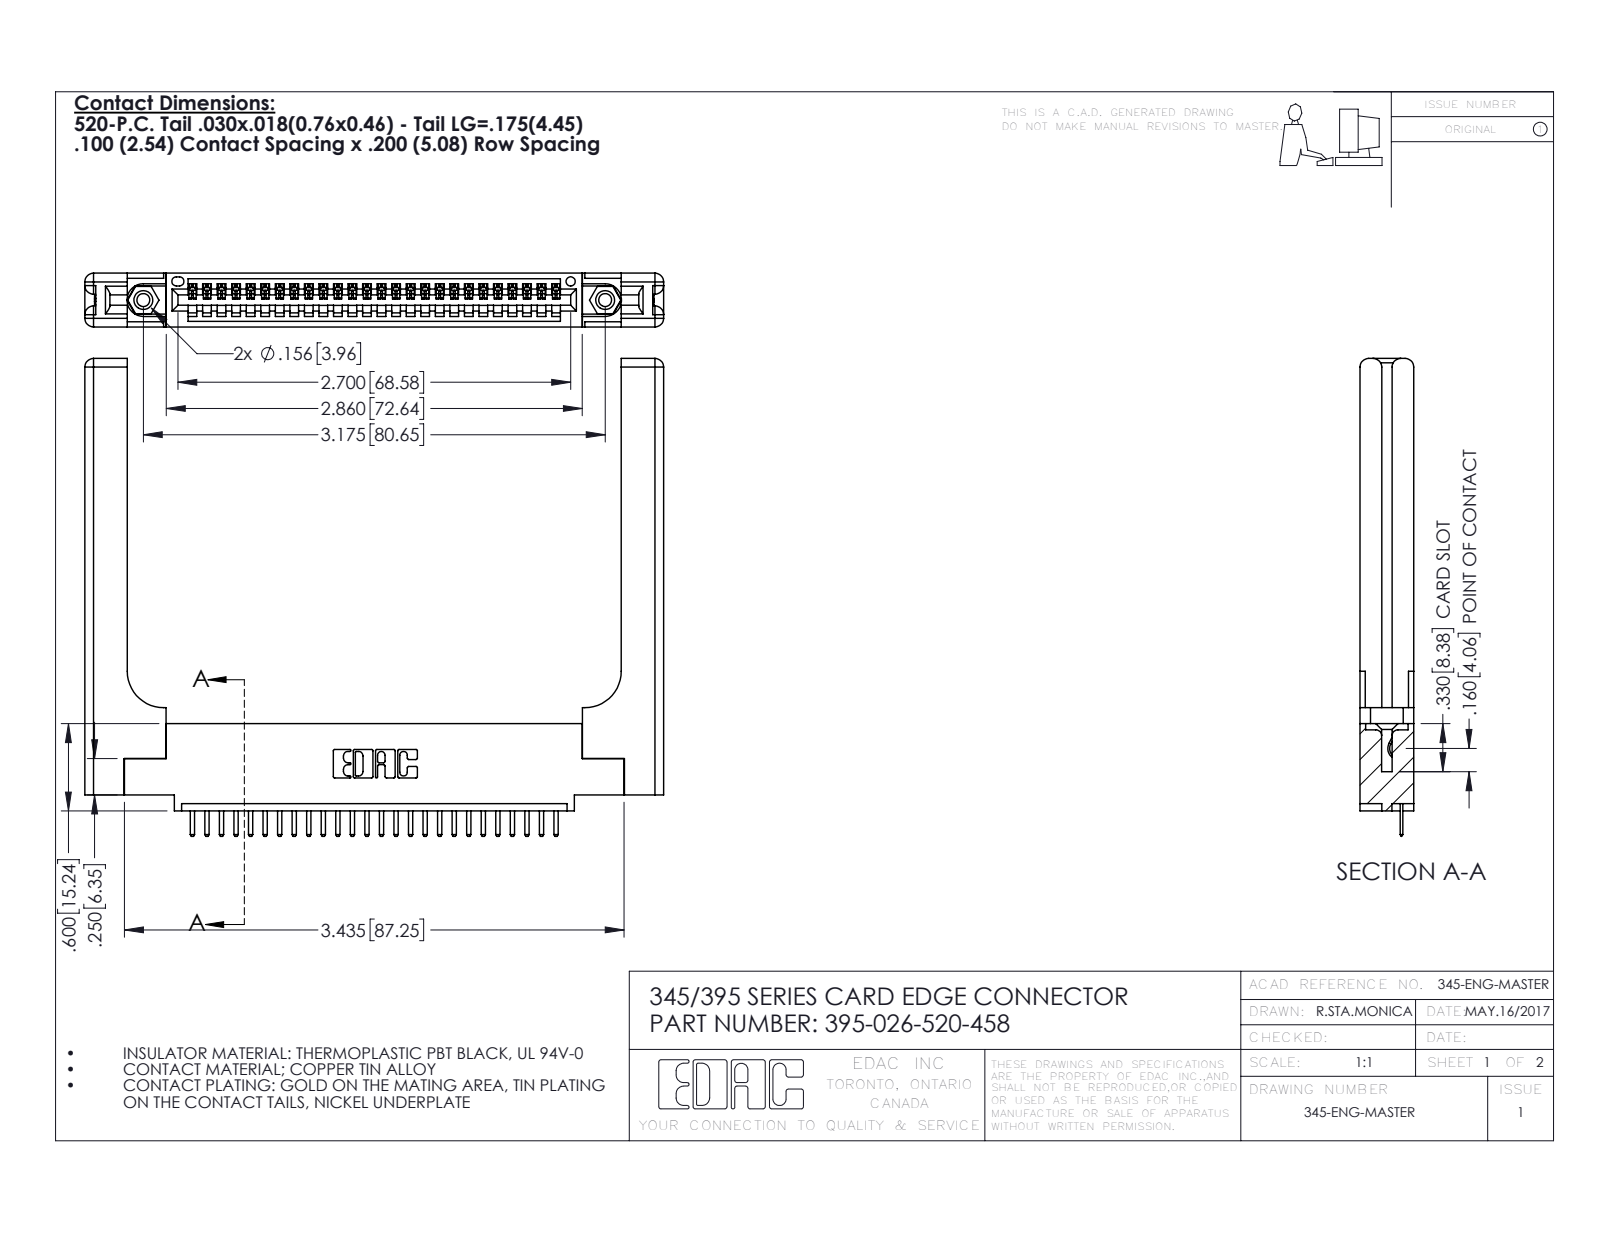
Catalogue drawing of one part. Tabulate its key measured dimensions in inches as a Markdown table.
| quantity | value |
| --- | --- |
| part name | 345 Part_0.110 Offset - 0.156 Dia-TH; 345-292-001_345-293-120; 395-026-520-458; 345-220-058_345-220-058 (+1 more) |
| STEP written by | SolidWorks 2016 (CONFIG_CONTROL_DESIGN) |
| units | inches |
| bodies | 31 solids, 1998 faces (1324 planar, 614 cylindrical, 60 other) |
| overall size | 3.979 × 3.285 × 0.37 |
| volume | 1.088 in³ |
| surface area | 26.83 in² |
| round holes (diameter × count) | 0.089 × 2, 0.125 × 2, 0.156 × 2, 0.064 × 1 |
| round bosses / shafts (diameter × count) | 0.155 × 2 |
| partial cylindrical surfaces (radius × count) | 0.01 × 54, 0.006 × 52, 0.01 × 22, 0.06 × 16, 0.007 × 6, 0.031 × 6, 0.026 × 3, 0.03 × 2 |
| main face-to-face distances | 0.37, 0.072, 0.298, 0.148, 0.15, 0.077, 0.22, 0.098, 0.272, 0.025 |
| hole center spacings | 0.27, 2.94, 3.175 |
